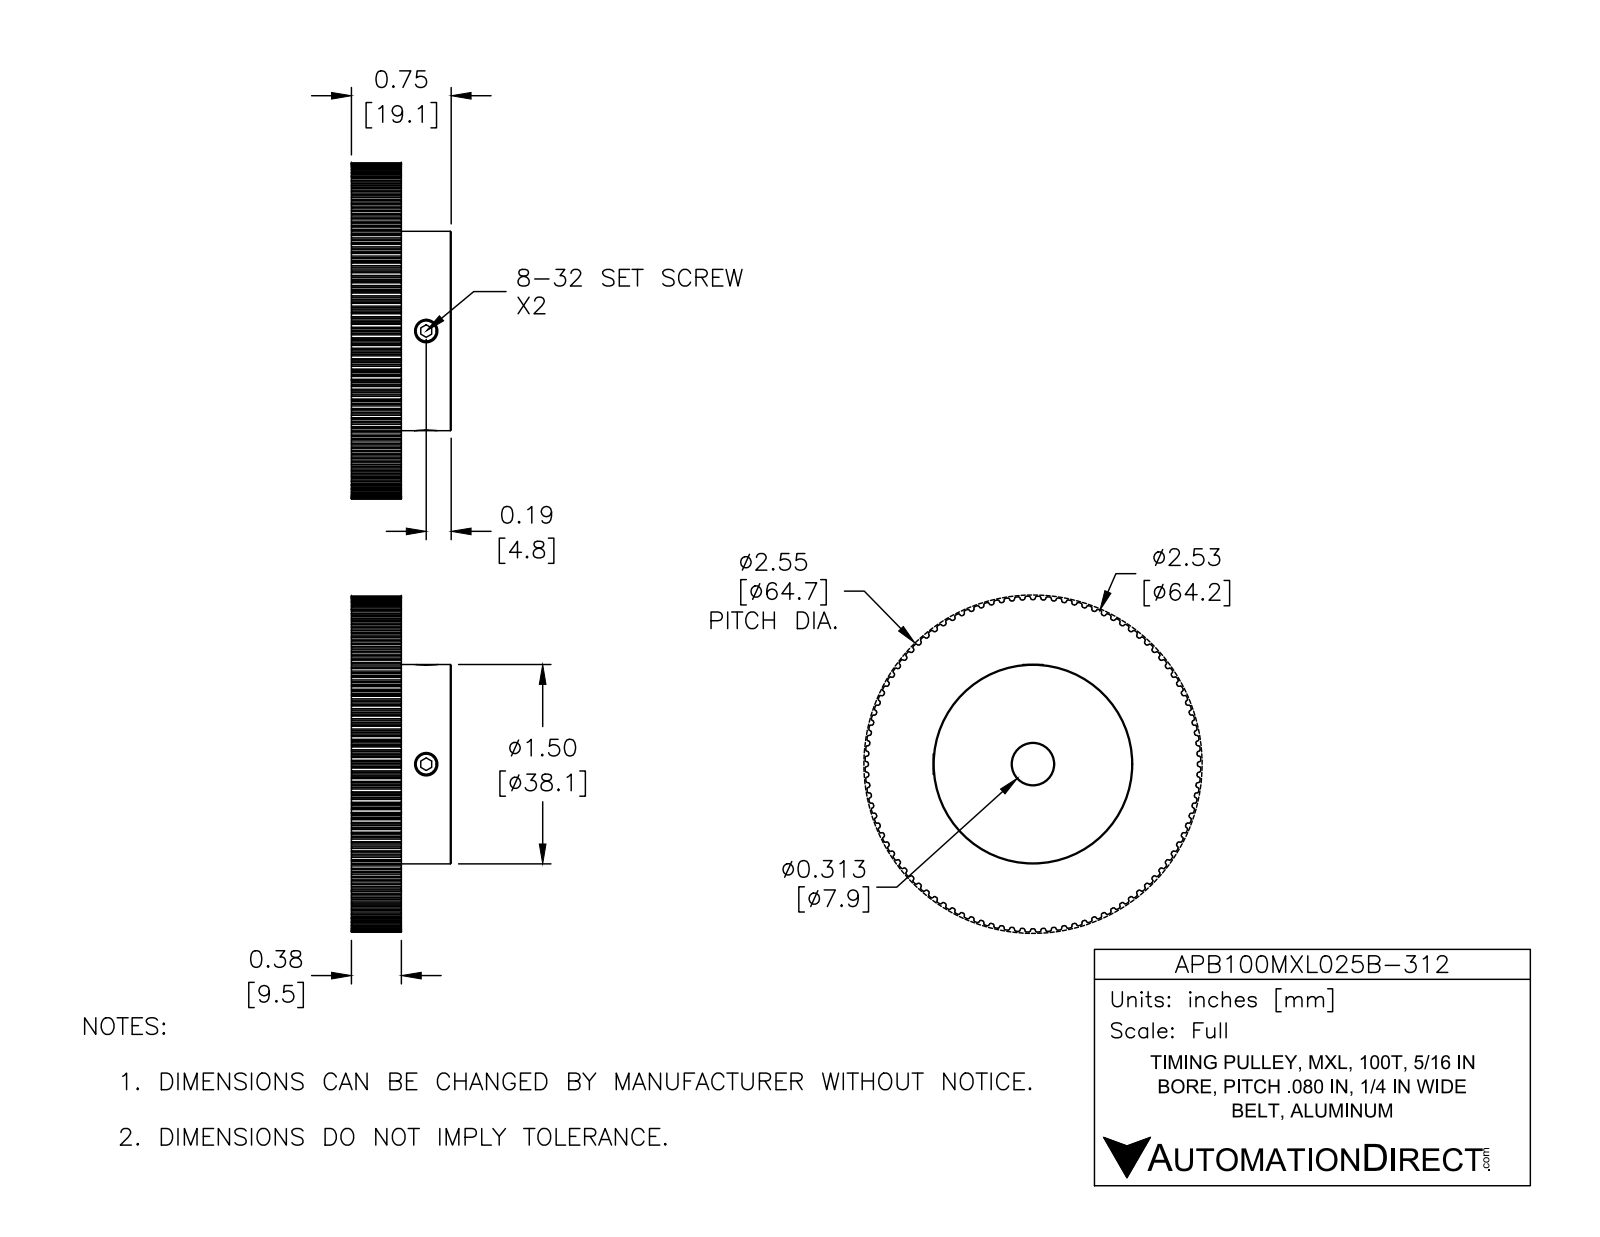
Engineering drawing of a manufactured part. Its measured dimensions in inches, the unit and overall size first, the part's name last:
Units: inches
Overall size (bounding box): 2.525 × 2.525 × 0.75
Round holes (diameter × count): ⌀0.164 ×2, ⌀0.313 ×1
Round bosses / shafts (diameter × count): ⌀0.16 ×2, ⌀1.5 ×1
Partial cylindrical surfaces — rounded edges, fillets, slot ends (radius × count): R0.009 ×200, R0.012 ×200, R1.263 ×1
Main face-to-face distances: 0.375, 0.75, 0.375, 0.821, 0.822, 0.82, 2.476, 2.476, 0.823, 2.477
Volume: 2.429 in³ · Surface area: 16.89 in²
Bodies: 3 solids, 925 faces (321 planar, 590 cylindrical, 14 other)
Part name (STEP PRODUCT): APB100MXL025B-312
STEP written by: SolidWorks 2016 (AUTOMOTIVE_DESIGN)
